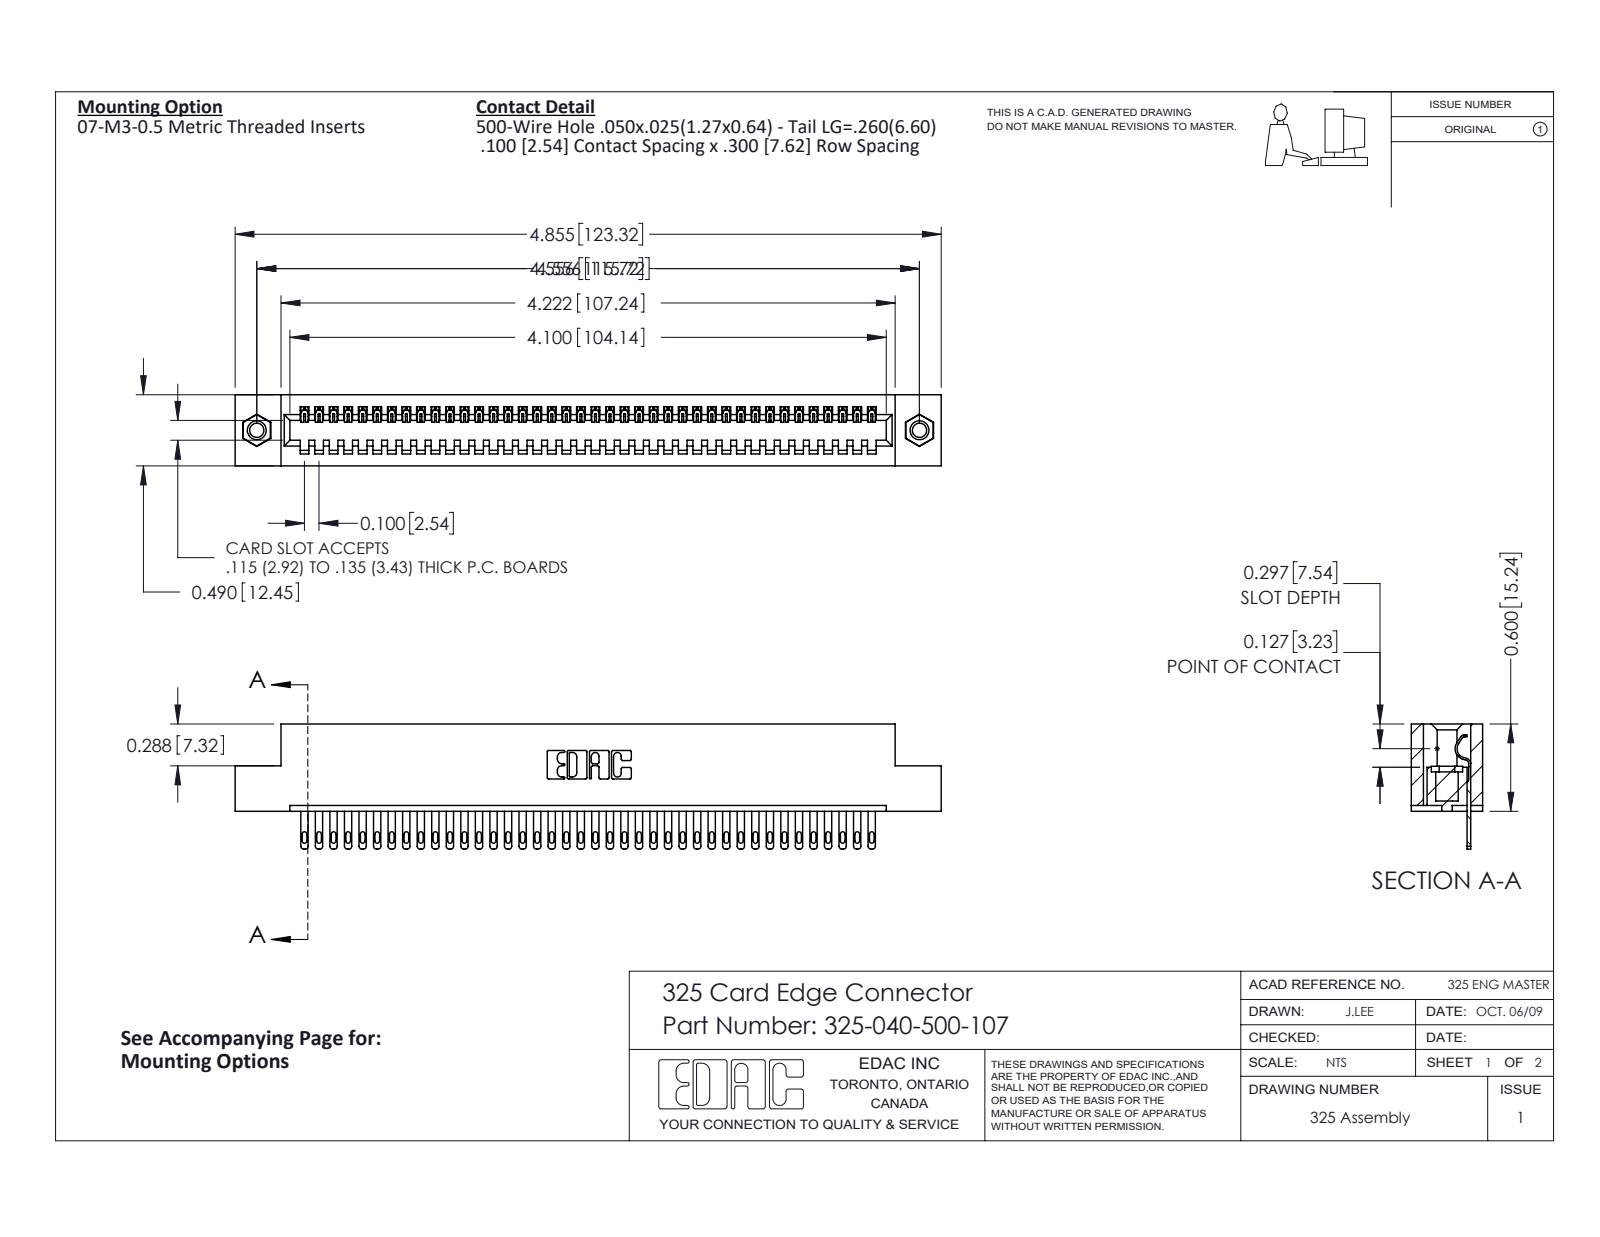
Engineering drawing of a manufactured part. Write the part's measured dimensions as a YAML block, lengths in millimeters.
part_name: "345-250-001_345-250-005-103; 325-292-001_325-293-100; 325 Part_TI; 325-040-500-107"
step_written_by: "SolidWorks 2016 (CONFIG_CONTROL_DESIGN)"
units: millimeters
bodies: {solids: 43, faces: 2334, planar: 1542, cylindrical: 776, other: 16}
overall_size: [123.3, 21.8, 12.4]
volume: 15600
surface_area: 17190
round_holes:
  - {diameter: 2.5, count: 2}
  - {diameter: 3.2, count: 2}
  - {diameter: 4.1, count: 2}
round_bosses_or_shafts:
  - {diameter: 3.9, count: 2}
partial_cylinders:
  - {radius: 0.2, count: 80}
  - {radius: 0.4, count: 80}
  - {radius: 0.5, count: 80}
  - {radius: 0.3, count: 22}
  - {radius: 0.2, count: 6}
  - {radius: 0.8, count: 6}
  - {radius: 0.7, count: 3}
  - {radius: 0.4, count: 1}
face_to_face_distances: [2.1, 10.3, 12.4, 7.6, 2.7, 9.7, 0.6, 8.3, 14.2, 6.7]
hole_center_spacings: [115.7]
